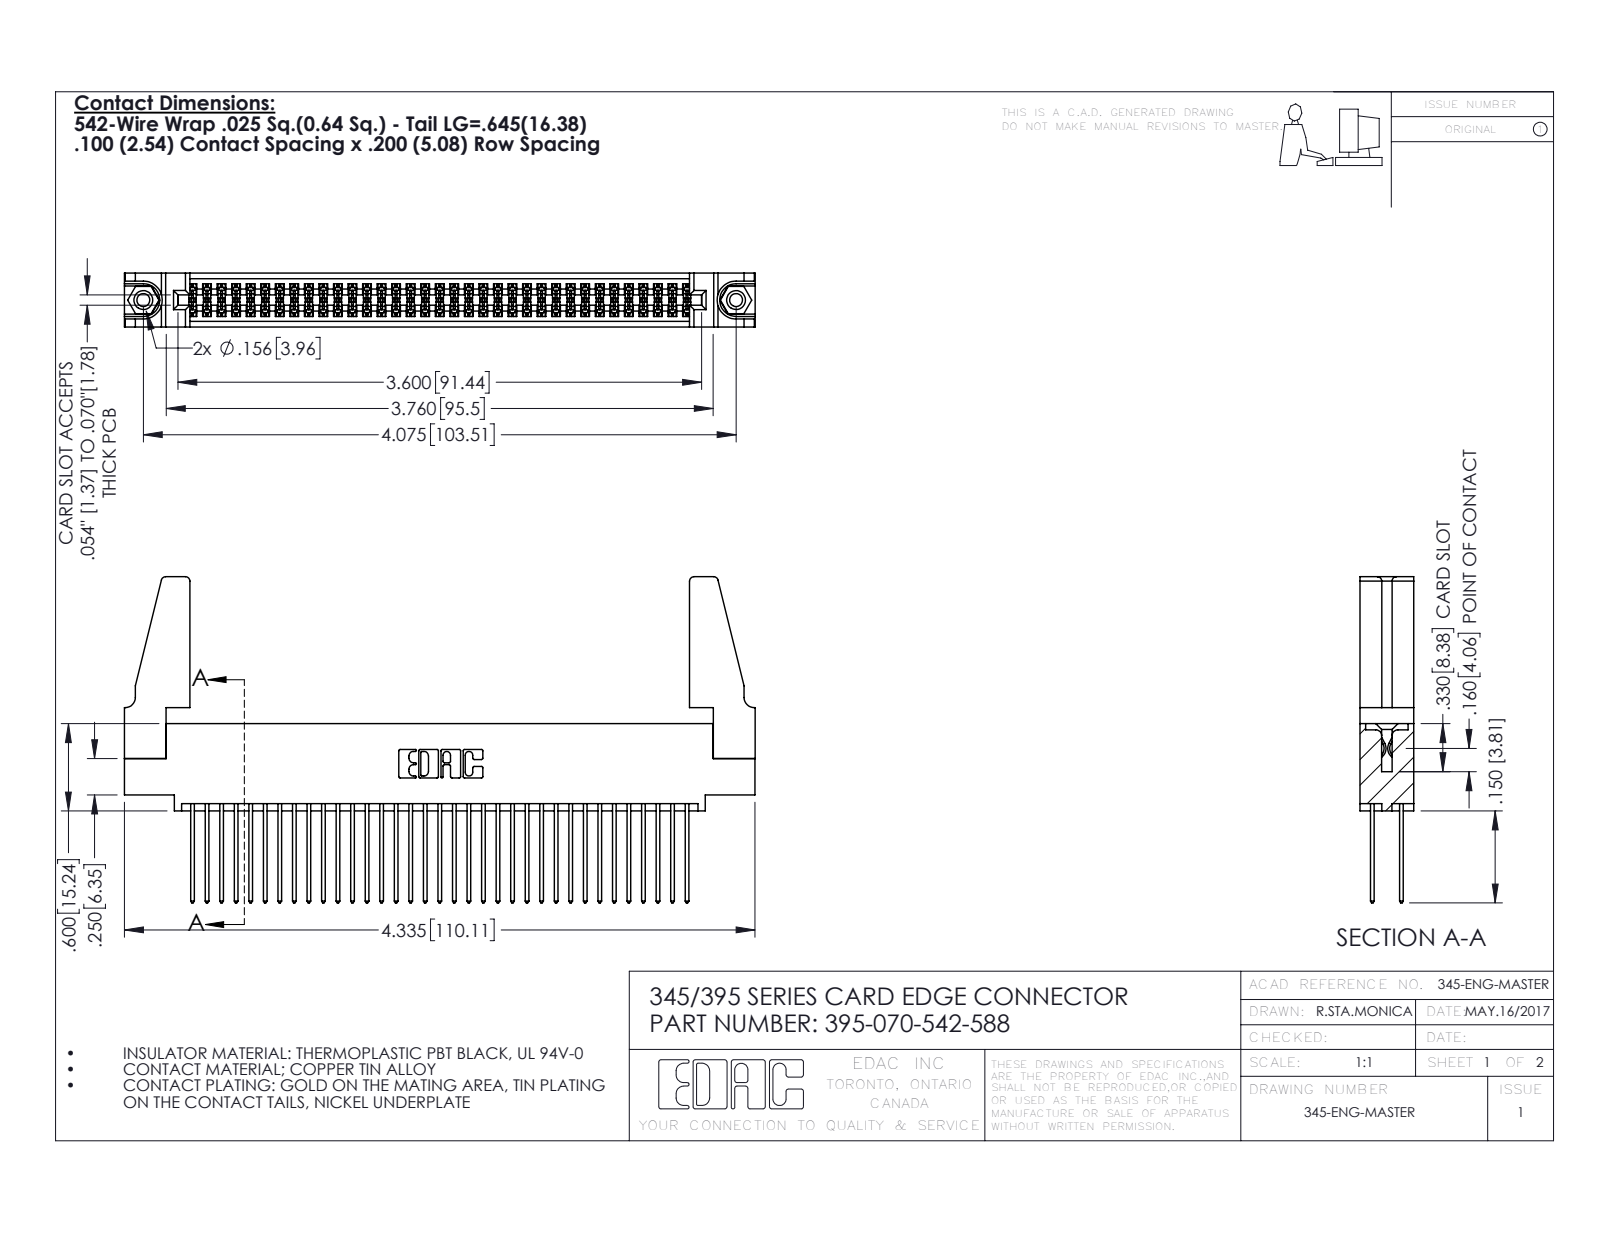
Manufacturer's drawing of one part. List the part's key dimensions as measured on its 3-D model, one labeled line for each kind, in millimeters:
Part name (STEP PRODUCT): 345 Part_0.110 Offset - 0.156 Dia-TH; 395-070-542-588; 345-220-078_345-220-088; 345-292-001_345-293-142 (+1 more)
STEP written by: SolidWorks 2016 (CONFIG_CONTROL_DESIGN)
Units: millimetres
Bodies: 75 solids, 3754 faces (2466 planar, 1272 cylindrical, 16 other)
Overall size (bounding box): 110.1 × 56.9 × 9.4
Volume: 14 100 mm³ · Surface area: 20 700 mm²
Round holes (diameter × count): ⌀2.3 ×2, ⌀3.2 ×2, ⌀4 ×2, ⌀1.6 ×1
Round bosses / shafts (diameter × count): ⌀3.9 ×2
Partial cylindrical surfaces — rounded edges, fillets, slot ends (radius × count): R0.2 ×105, R0.3 ×70, R0.3 ×22, R0.8 ×8, R0.2 ×6, R0.8 ×6, R0.7 ×3, R0.4 ×2
Main face-to-face distances: 1.8, 7.6, 5.1, 2.5, 6.9, 0.6, 9.4, 5.7, 4.4, 3.8
Hole centre spacings: 6.9, 97.5, 103.5
